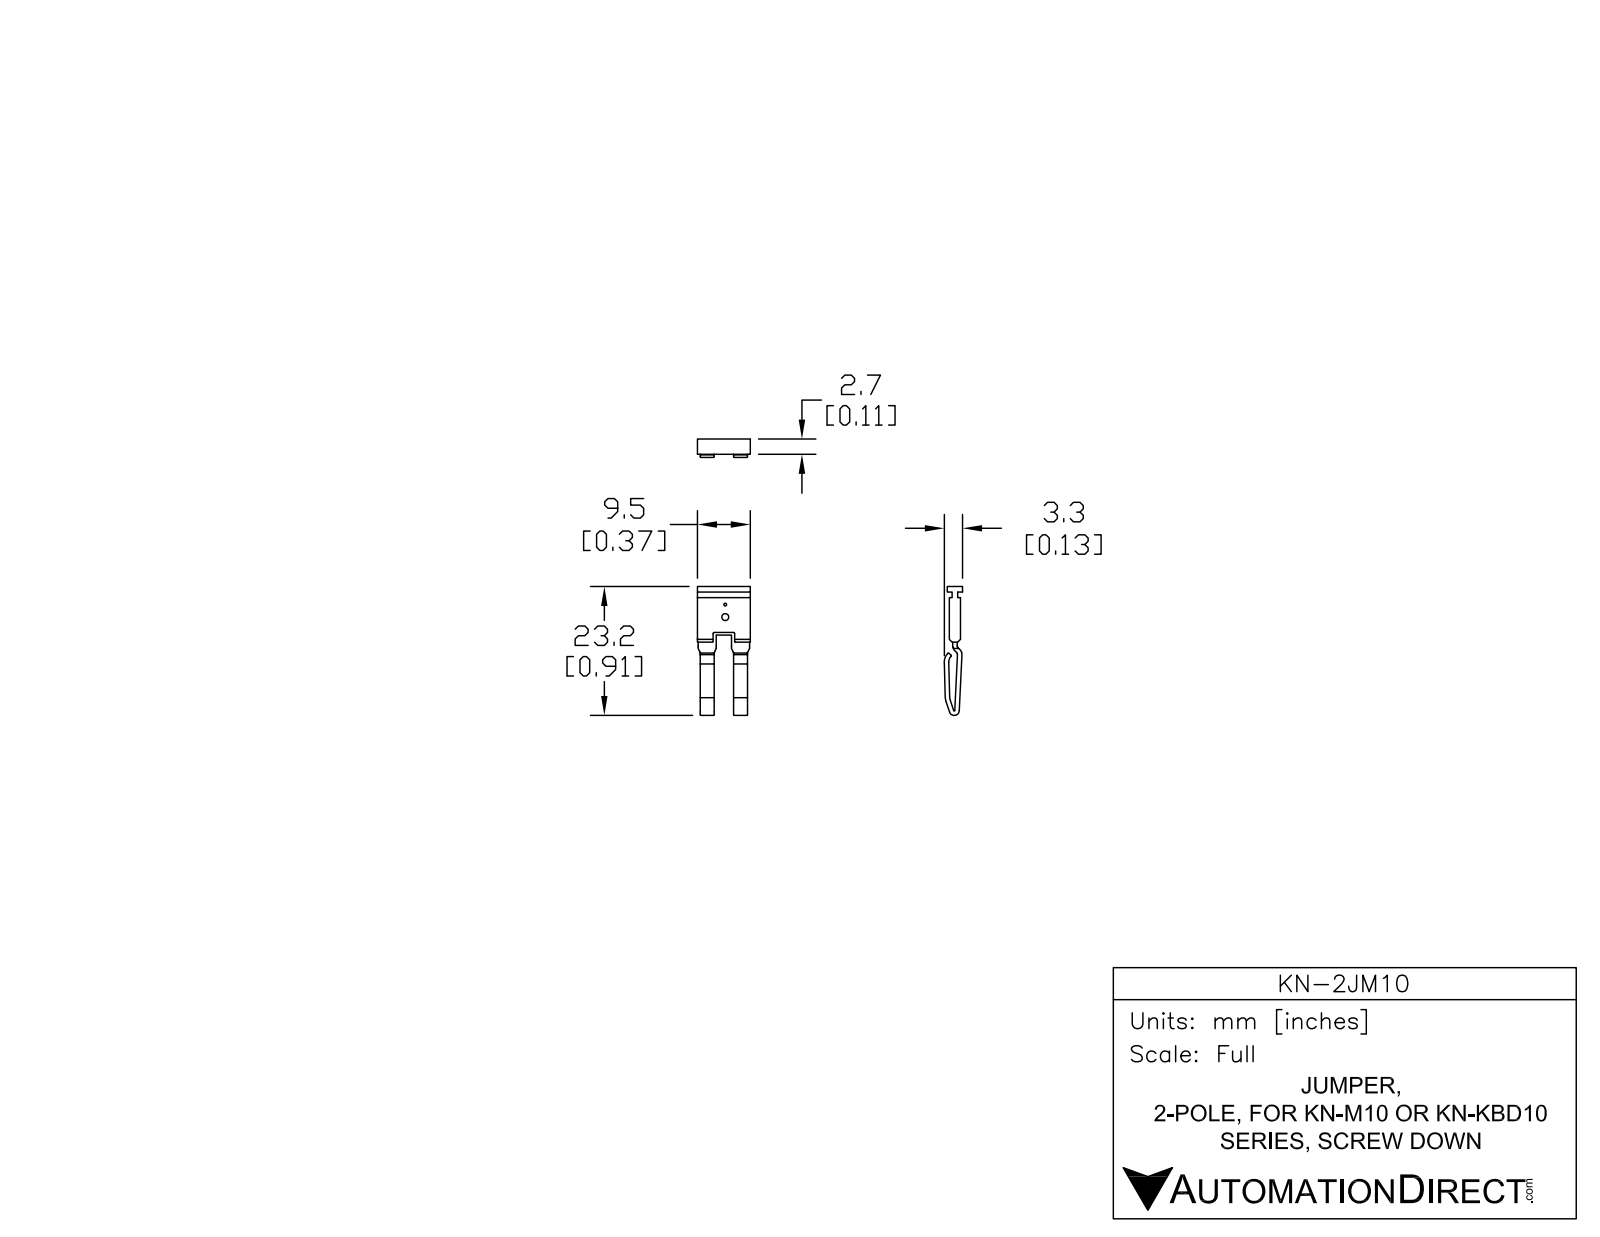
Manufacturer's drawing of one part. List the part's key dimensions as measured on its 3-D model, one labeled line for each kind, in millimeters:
Part name (STEP PRODUCT): KN-2JM10
STEP written by: SolidWorks 2014 (AUTOMOTIVE_DESIGN)
Units: millimetres
Bodies: 1 solid, 224 faces (68 planar, 86 cylindrical, 70 other)
Overall size (bounding box): 23.19 × 9.5 × 3.3
Volume: 272 mm³ · Surface area: 623 mm²
Round holes (diameter × count): ⌀0.5 ×1, ⌀1.25 ×1
Partial cylindrical surfaces — rounded edges, fillets, slot ends (radius × count): R0.12 ×50, R0.25 ×2, R0.6 ×2, R1.4 ×2, R1.6 ×2, R2.4 ×2, R0.1 ×1, R0.9 ×1
Main face-to-face distances: 2, 0.8, 0.5, 1, 9, 6.5, 2.5, 6, 3, 9.5
Hole centre spacings: 2.25
